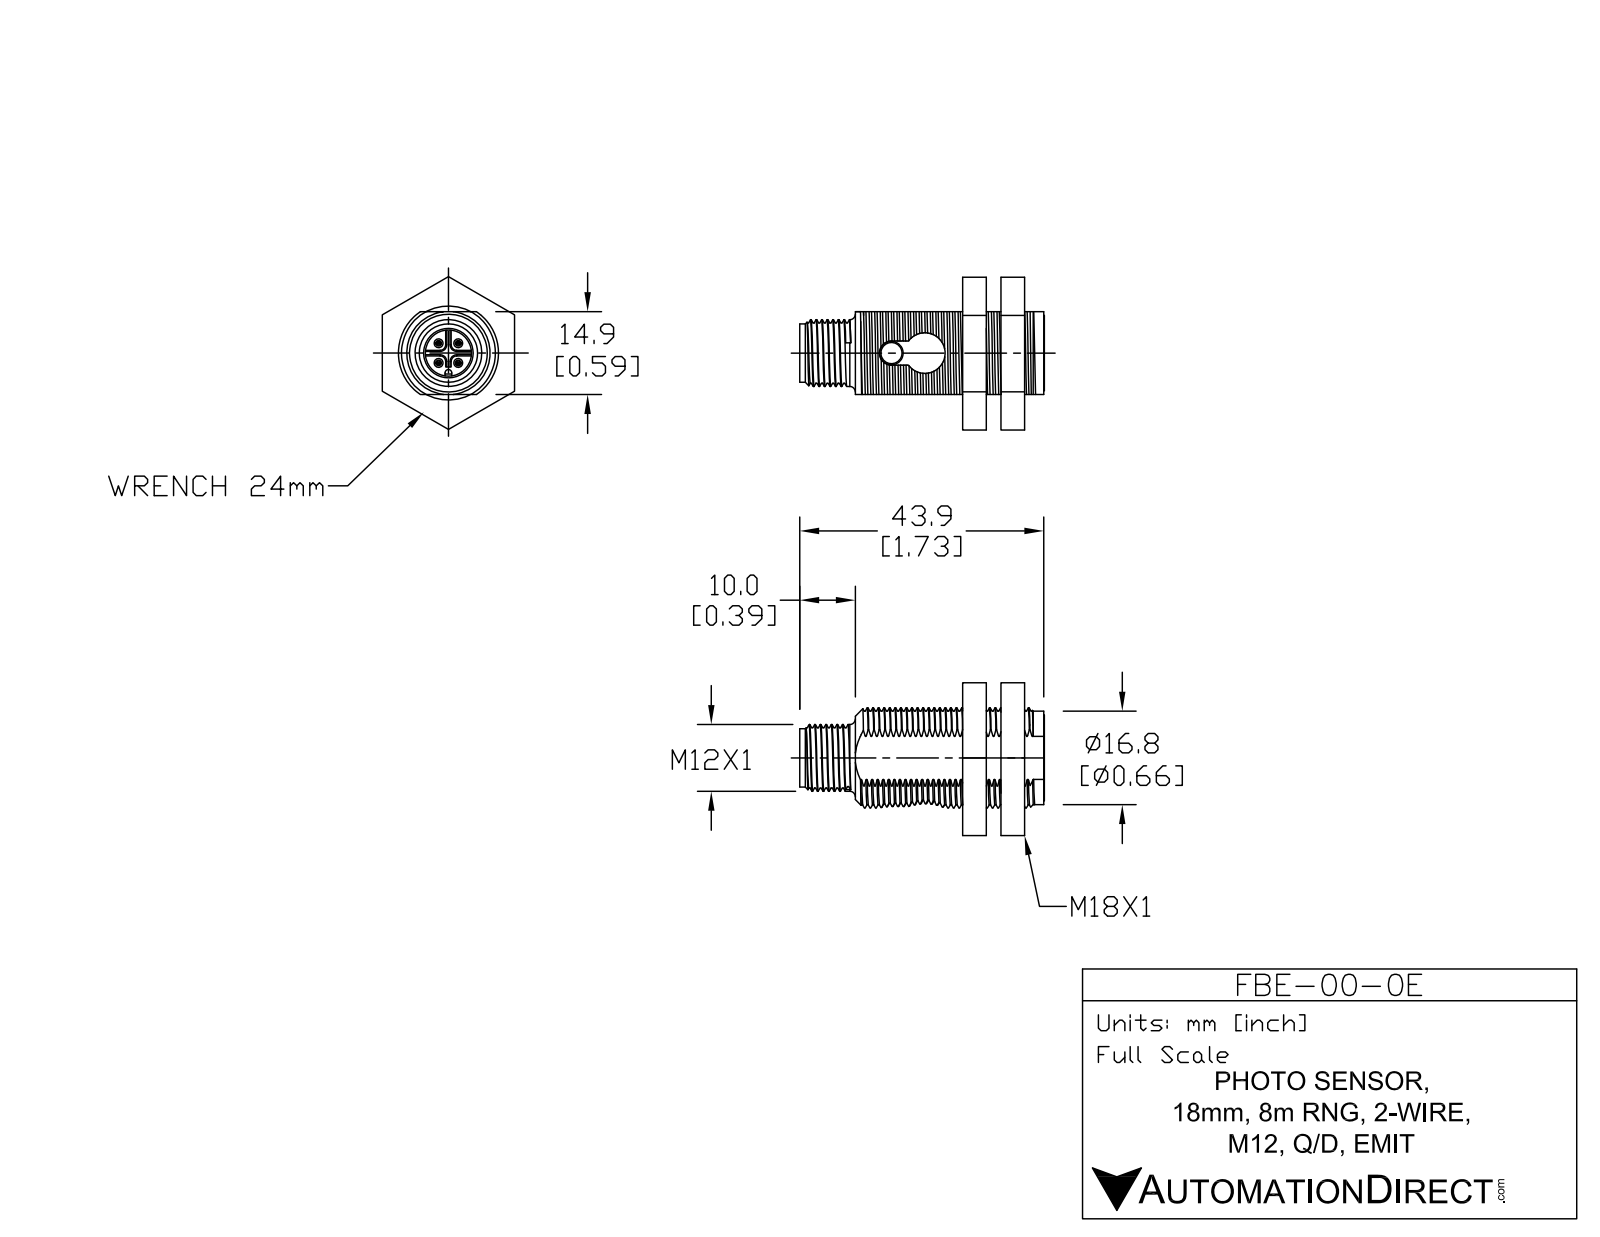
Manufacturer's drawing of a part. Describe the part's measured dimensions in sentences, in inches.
The part is named "FBE-00-0E". Its 3-D file was written by "SolidWorks 2011 (AUTOMOTIVE_DESIGN)". It is 6 solids with 209 faces: 114 planar, 28 cylindrical and 67 other. Overall it measures 1.728 by 1.09 by 0.967 inches. Its volume is 0.628 cubic inches and its surface area 7.911 square inches. Round holes: 1 of diameter 0.285, 1 of diameter 0.331. Round bosses or shafts: 4 of diameter 0.039, 1 of diameter 0.472, 1 of diameter 0.409. Partial cylindrical surfaces (rounded edges, fillets, slot ends): 2 of radius 0.254, 2 of radius 0.294, 1 of radius 0.02, 1 of radius 0.084, 1 of radius 0.331, 1 of radius 0.335, 1 of radius 0.354. The main face-to-face distances are 0.315, 0.177, 0.945, 0.591, 0.039, 0.492, 0.508, 0.547, 0.193, 0.232.
